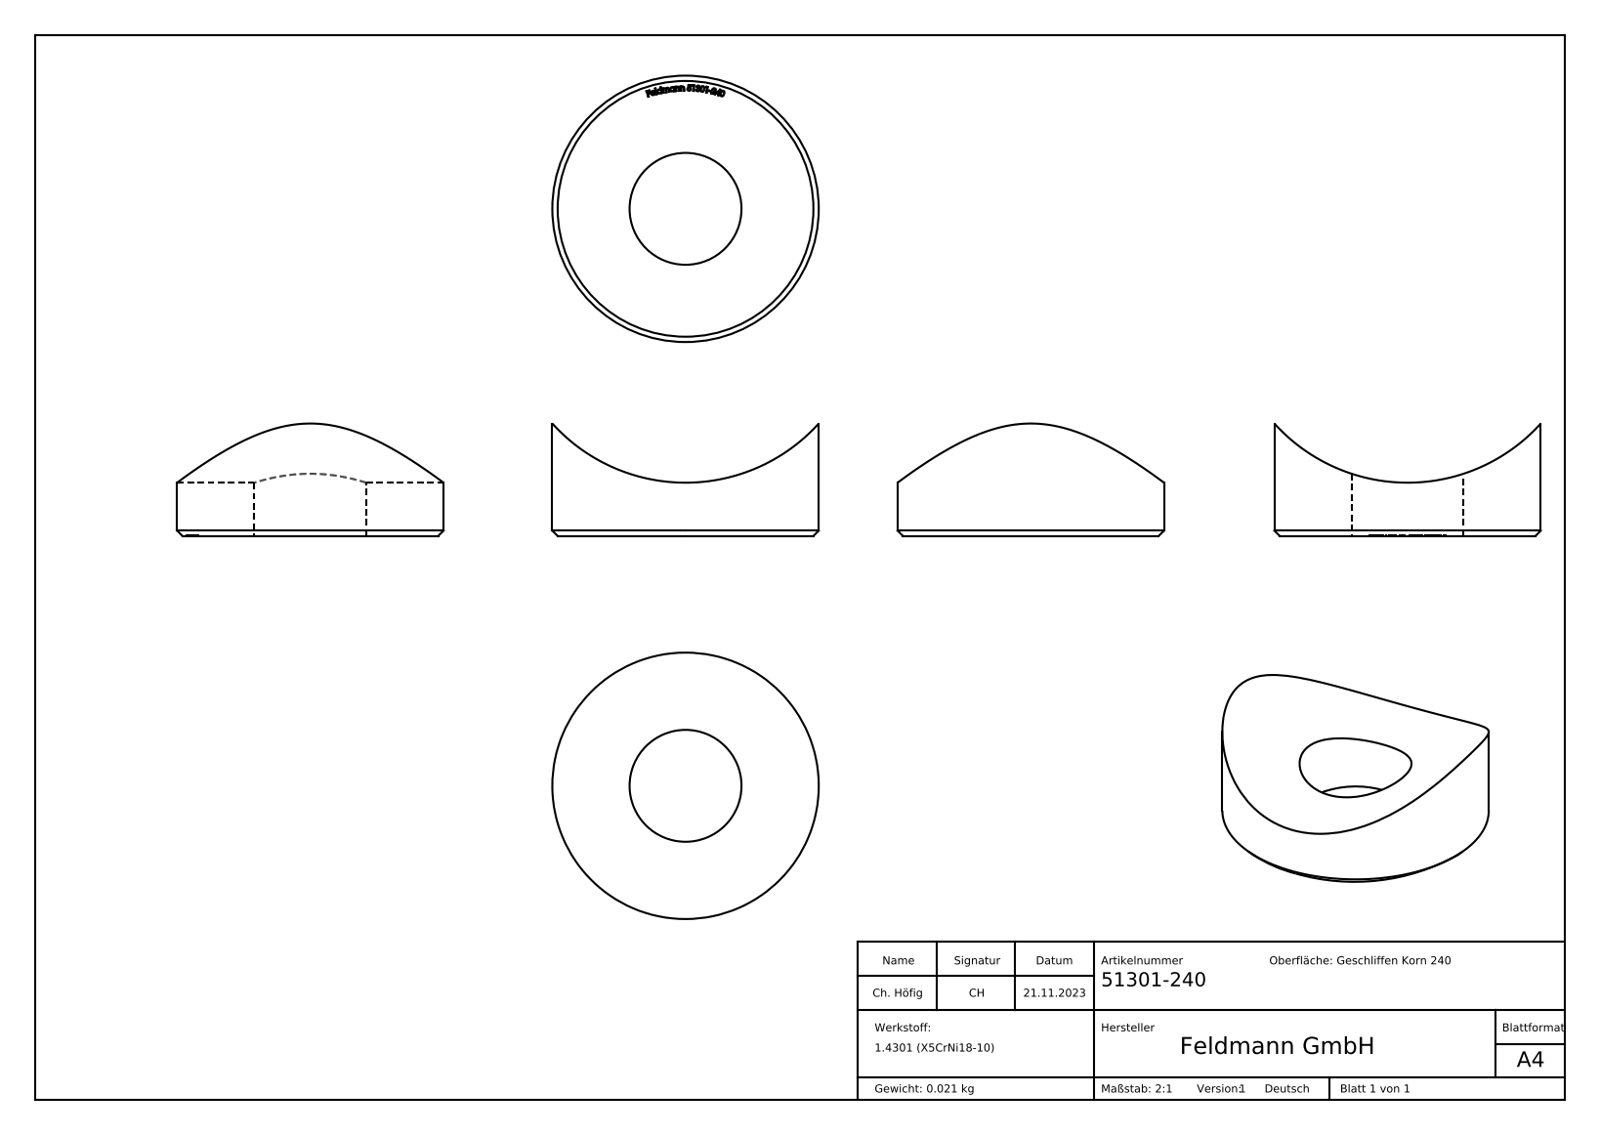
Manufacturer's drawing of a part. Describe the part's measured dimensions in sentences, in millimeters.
The part is named "51301-240". Its 3-D file was written by "SolidWorks 2018 (CONFIG_CONTROL_DESIGN)". It is 1 solid with 220 faces: 122 planar, 3 cylindrical and 95 other. Overall it measures 25 by 25 by 10.55 millimeters. Its volume is 2 611 cubic millimeters and its surface area 1 610 square millimeters. Round holes: 1 of diameter 10.5. Round bosses or shafts: 1 of diameter 25. Partial cylindrical surfaces (rounded edges, fillets, slot ends): 1 of radius 16.85. The main face-to-face distances are 0.54, 0.49, 0.59, 0.34, 0.32, 0.39, 0.48, 0.52, 0.36, 0.31.
